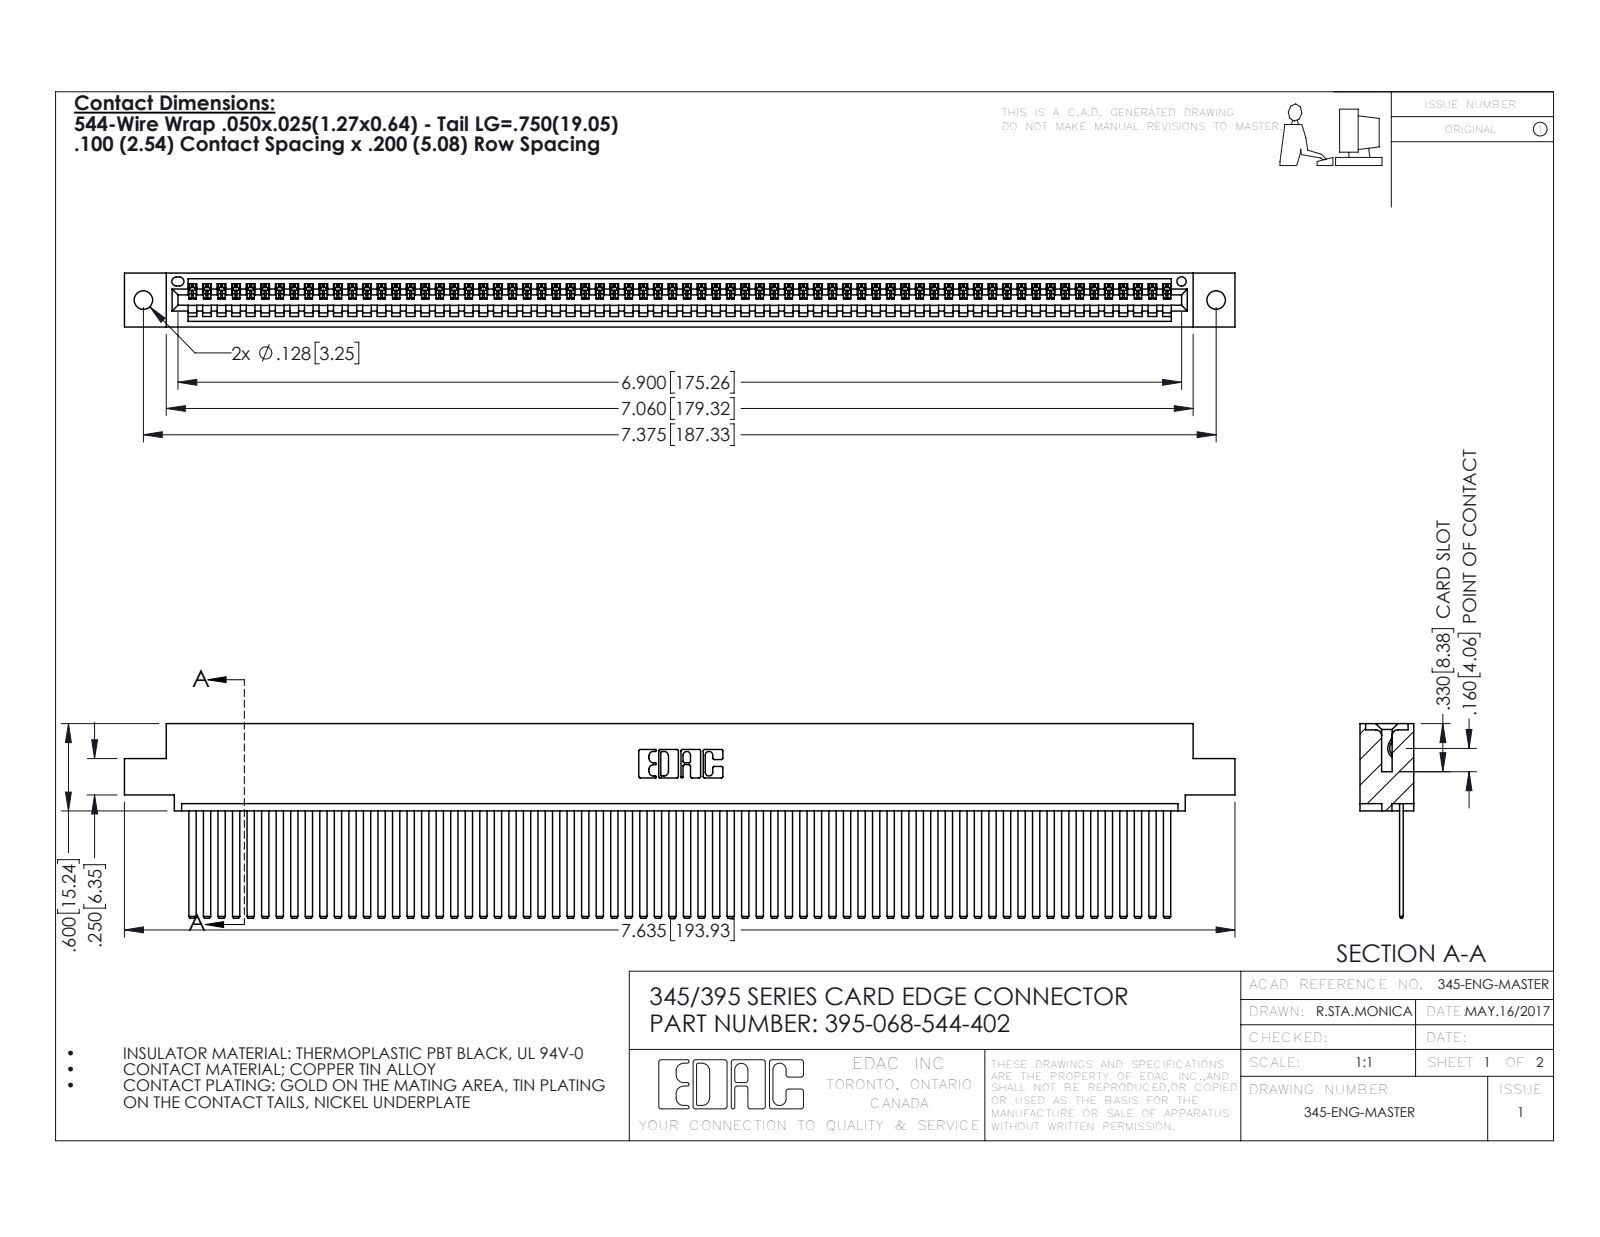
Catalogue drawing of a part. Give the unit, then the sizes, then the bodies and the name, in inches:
Units: inches
Overall size (bounding box): 7.635 × 1.337 × 0.37
Round holes (diameter × count): ⌀0.128 ×2, ⌀0.064 ×1
Partial cylindrical surfaces — rounded edges, fillets, slot ends (radius × count): R0.006 ×136, R0.01 ×22, R0.007 ×6, R0.031 ×6, R0.026 ×3, R0.031 ×2, R0.04 ×2, R0.014 ×1
Main face-to-face distances: 0.072, 0.298, 0.025, 0.098, 0.272, 0.37, 0.2, 0.225, 0.149, 0.072
Hole centre spacings: 0.27, 7.139, 7.375
Volume: 1.178 in³ · Surface area: 43.69 in²
Bodies: 69 solids, 3666 faces (2532 planar, 1134 cylindrical, 0 other)
Part name (STEP PRODUCT): 395-068-544-402; 345 Part_0.110 Offset - 0.128 Dia; 345-292-001_345-293-144
STEP written by: SolidWorks 2016 (CONFIG_CONTROL_DESIGN)
